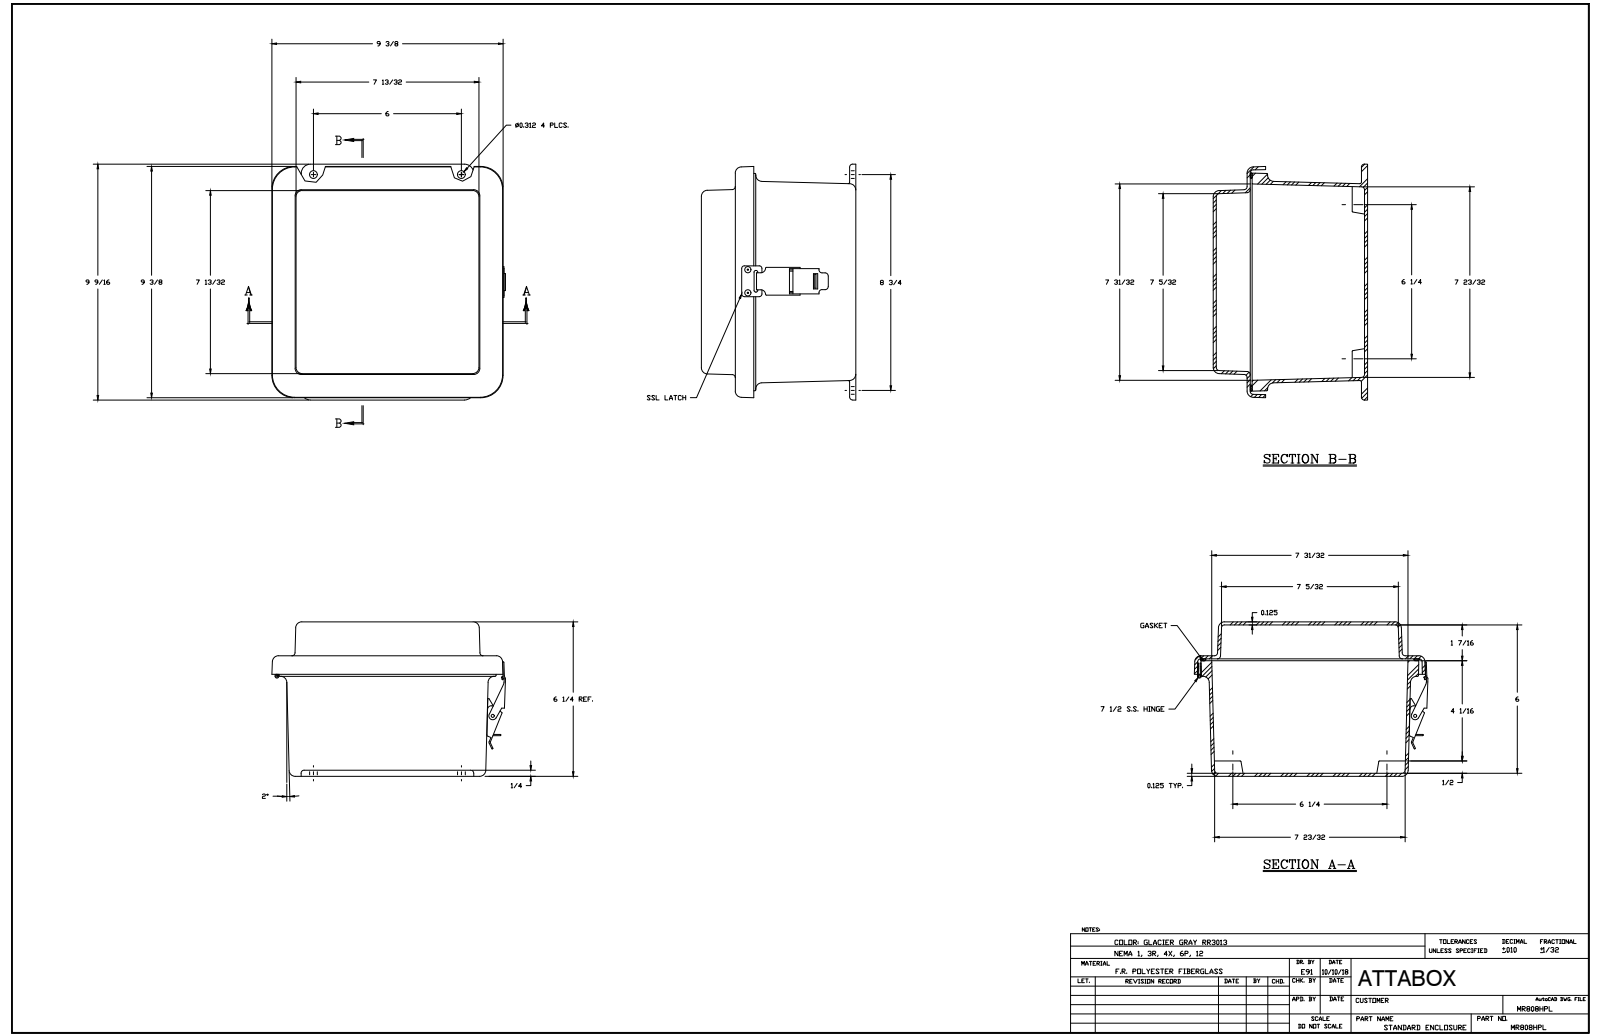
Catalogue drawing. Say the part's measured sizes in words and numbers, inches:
The part is named "MR808HPL". Its 3-D file was written by "SolidWorks 2018 (AUTOMOTIVE_DESIGN)". It is 25 solids with 823 faces: 300 planar, 327 cylindrical and 196 other. Overall it measures 9.562 by 9.529 by 6.262 inches. Its volume is 56.33 cubic inches and its surface area 820.8 square inches. Round holes: 12 of diameter 0.14, 8 of diameter 0.152, 6 of diameter 0.131, 4 of diameter 0.104, 4 of diameter 0.156, 4 of diameter 0.218, 2 of diameter 0.13, 2 of diameter 0.135, 1 of diameter 0.085, 1 of diameter 0.085, 1 of diameter 0.375. Round bosses or shafts: 5 of diameter 0.25, 5 of diameter 0.125, 4 of diameter 0.27, 4 of diameter 0.125, 1 of diameter 0.3, 1 of diameter 0.17, 1 of diameter 0.155, 1 of diameter 0.135. Partial cylindrical surfaces (rounded edges, fillets, slot ends): 36 of radius 0.031, 28 of radius 0.125, 16 of radius 0.25, 12 of radius 0.015, 8 of radius 0.045, 6 of radius 0.03, 6 of radius 0.2, 5 of radius 0.022. The main face-to-face distances are 0.125, 0.125, 6.137, 6.012, 6.263, 4.637, 4.763, 1.375, 1.5, 4.887. The hole center spacings are 7.249, 3.5, 0.937, 1.326, 6.25, 8.125, 10.165, 0.25.
